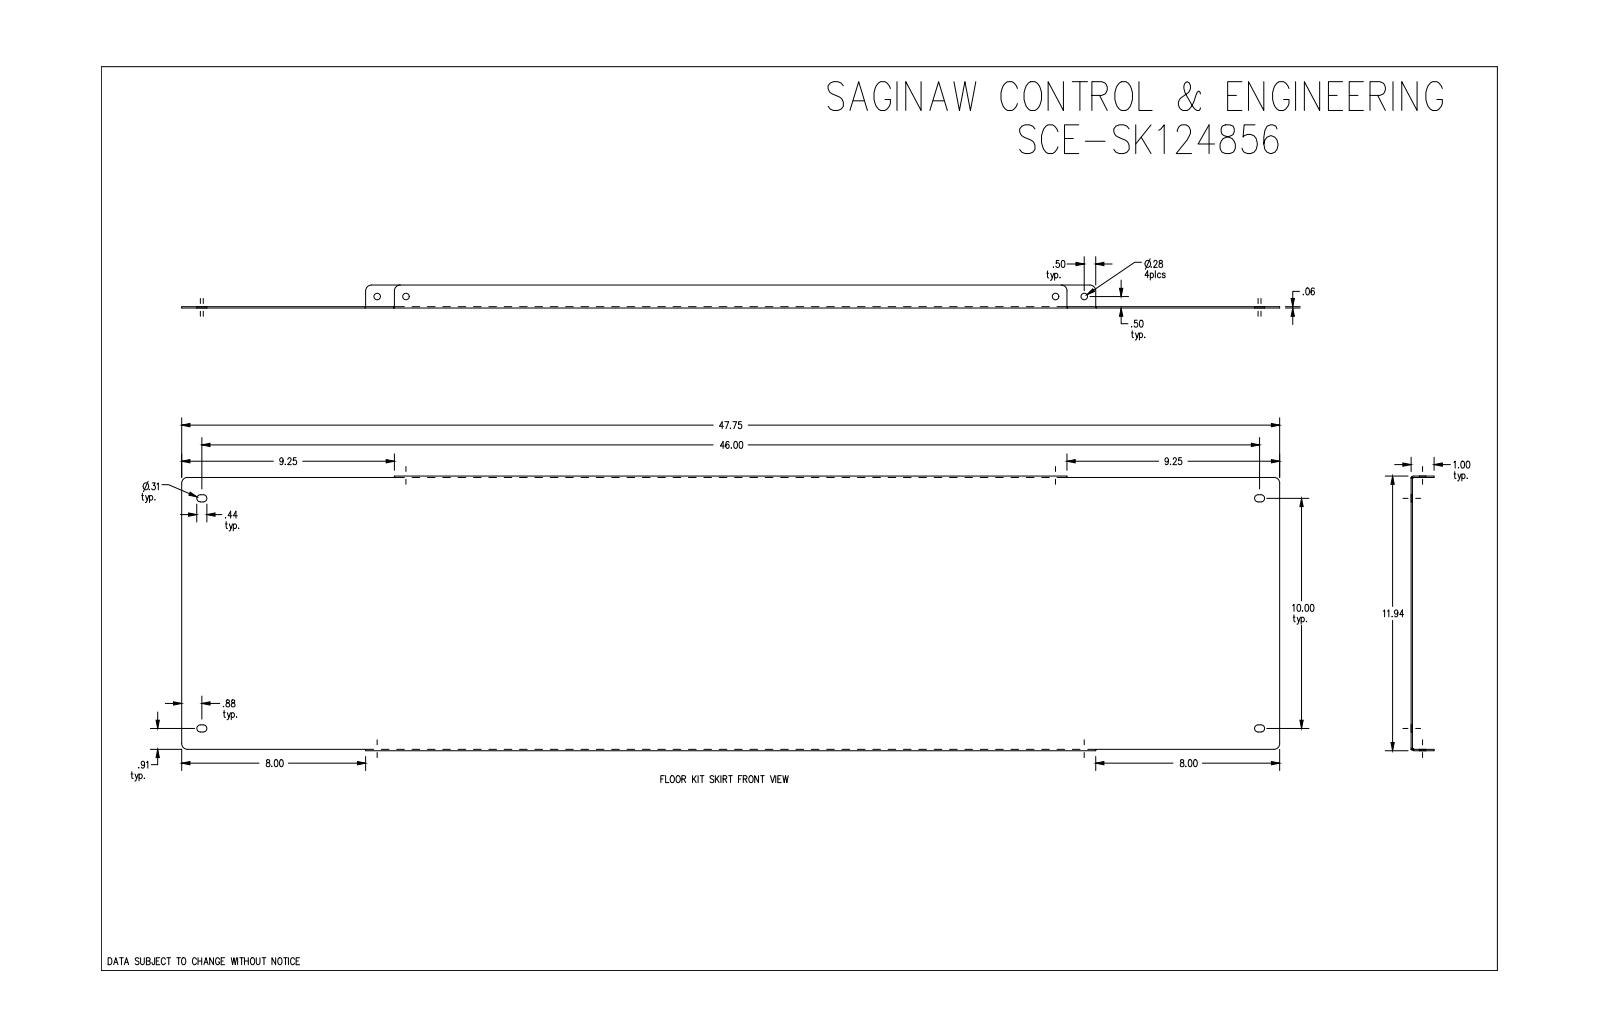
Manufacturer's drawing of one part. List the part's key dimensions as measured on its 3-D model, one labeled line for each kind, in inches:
Part name (STEP PRODUCT): SCE-SK124856
STEP written by: SolidWorks 2019 (CONFIG_CONTROL_DESIGN)
Units: inches
Bodies: 1 solid, 62 faces (26 planar, 24 cylindrical, 12 other)
Overall size (bounding box): 47.75 × 11.938 × 1
Volume: 37.33 in³ · Surface area: 1 252 in²
Round holes (diameter × count): ⌀0.281 ×4
Partial cylindrical surfaces — rounded edges, fillets, slot ends (radius × count): R0.156 ×8, R0.25 ×8, R0.06 ×2, R0.12 ×2
Main face-to-face distances: 0.06, 0.06, 11.878, 11.817, 11.938, 0.94, 1, 47.75, 9.25, 38.5
Hole centre spacings: 1.25, 29.5, 28.25, 30.75
